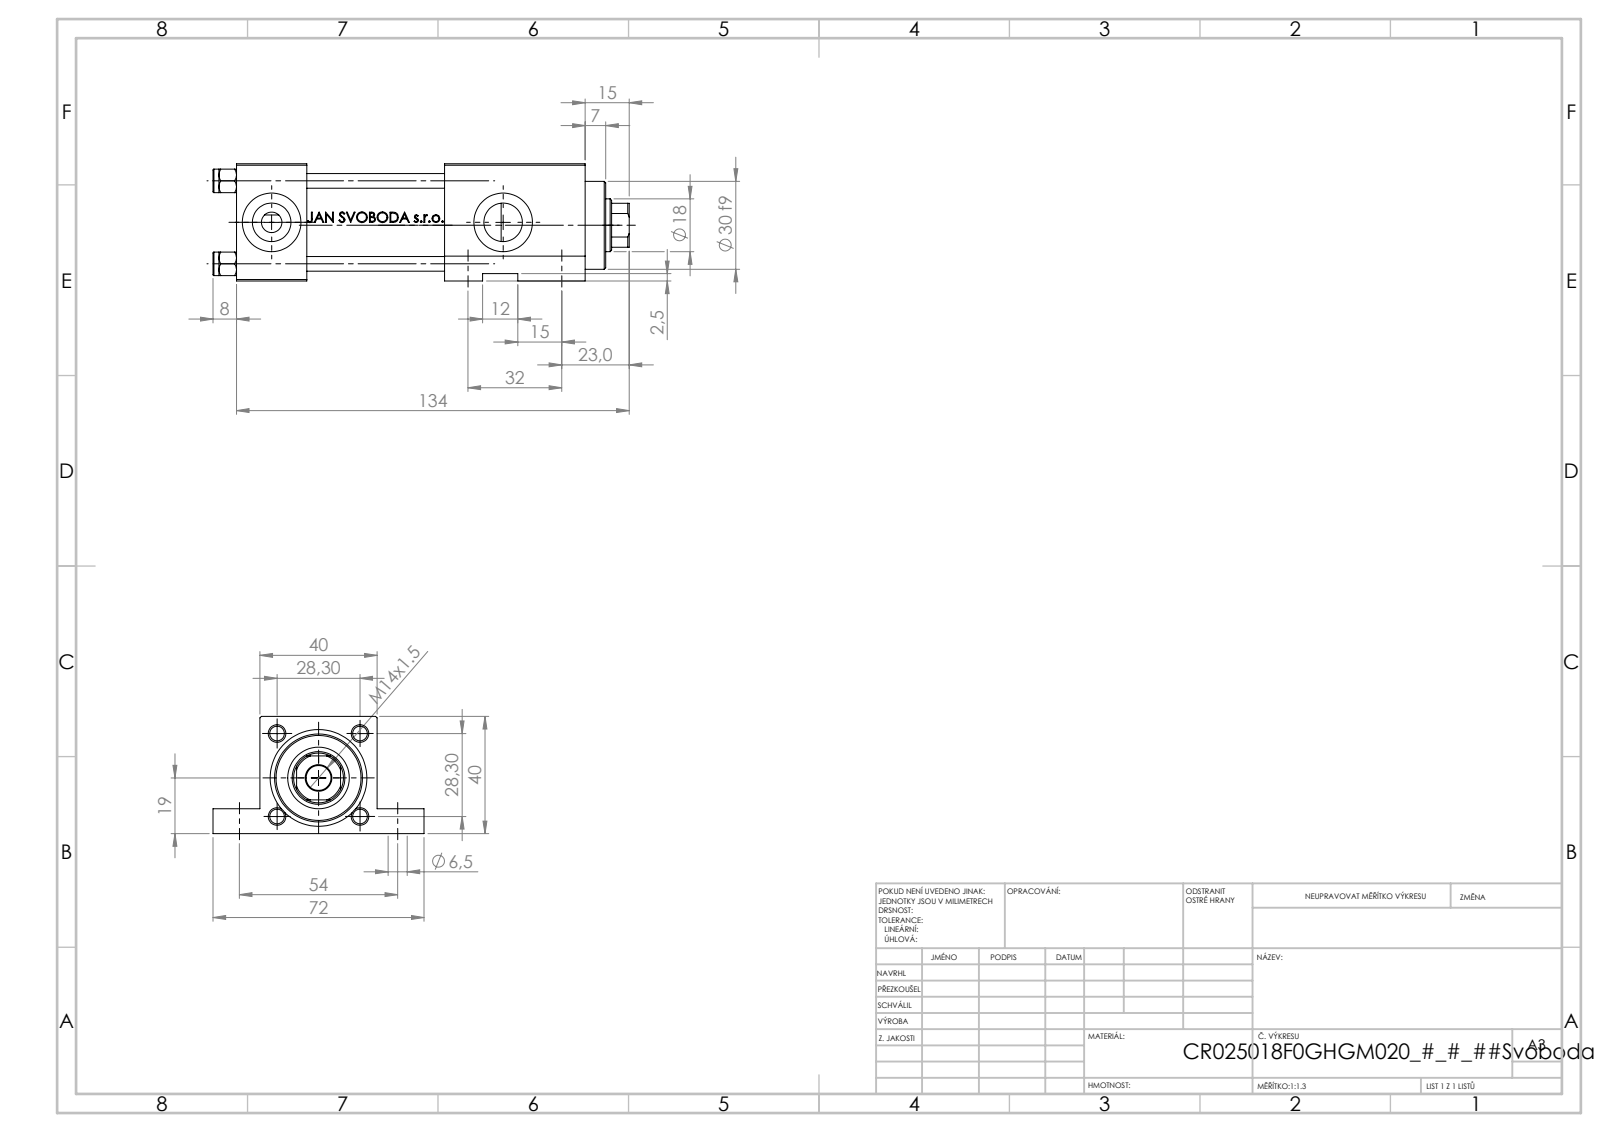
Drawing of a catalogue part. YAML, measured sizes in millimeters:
part_name: "V215CR_F_TYCINKA; V215CR_F_Body; V215CR_VCP_F; NUT_M5_F (+1 more)"
step_written_by: "SolidWorks 2019 (CONFIG_CONTROL_DESIGN)"
units: millimeters
bodies: {solids: 11, faces: 1099, planar: 435, cylindrical: 124, other: 540}
overall_size: [142, 72, 40]
volume: 160129
surface_area: 60719
round_holes:
  - {diameter: 5, count: 4}
  - {diameter: 6.5, count: 4}
  - {diameter: 20, count: 3}
  - {diameter: 7, count: 2}
  - {diameter: 13.16, count: 2}
  - {diameter: 8.5, count: 1}
  - {diameter: 18, count: 1}
  - {diameter: 21, count: 1}
  - {diameter: 25, count: 1}
  - {diameter: 30, count: 1}
round_bosses_or_shafts:
  - {diameter: 8, count: 4}
  - {diameter: 31, count: 1}
partial_cylinders:
  - {radius: 8.5, count: 1}
face_to_face_distances: [40, 24, 8.5, 31.5, 71, 47, 48, 6, 119, 95]
hole_center_spacings: [28.3, 19.32, 20.73, 32, 40.02, 54, 62.77, 79]
